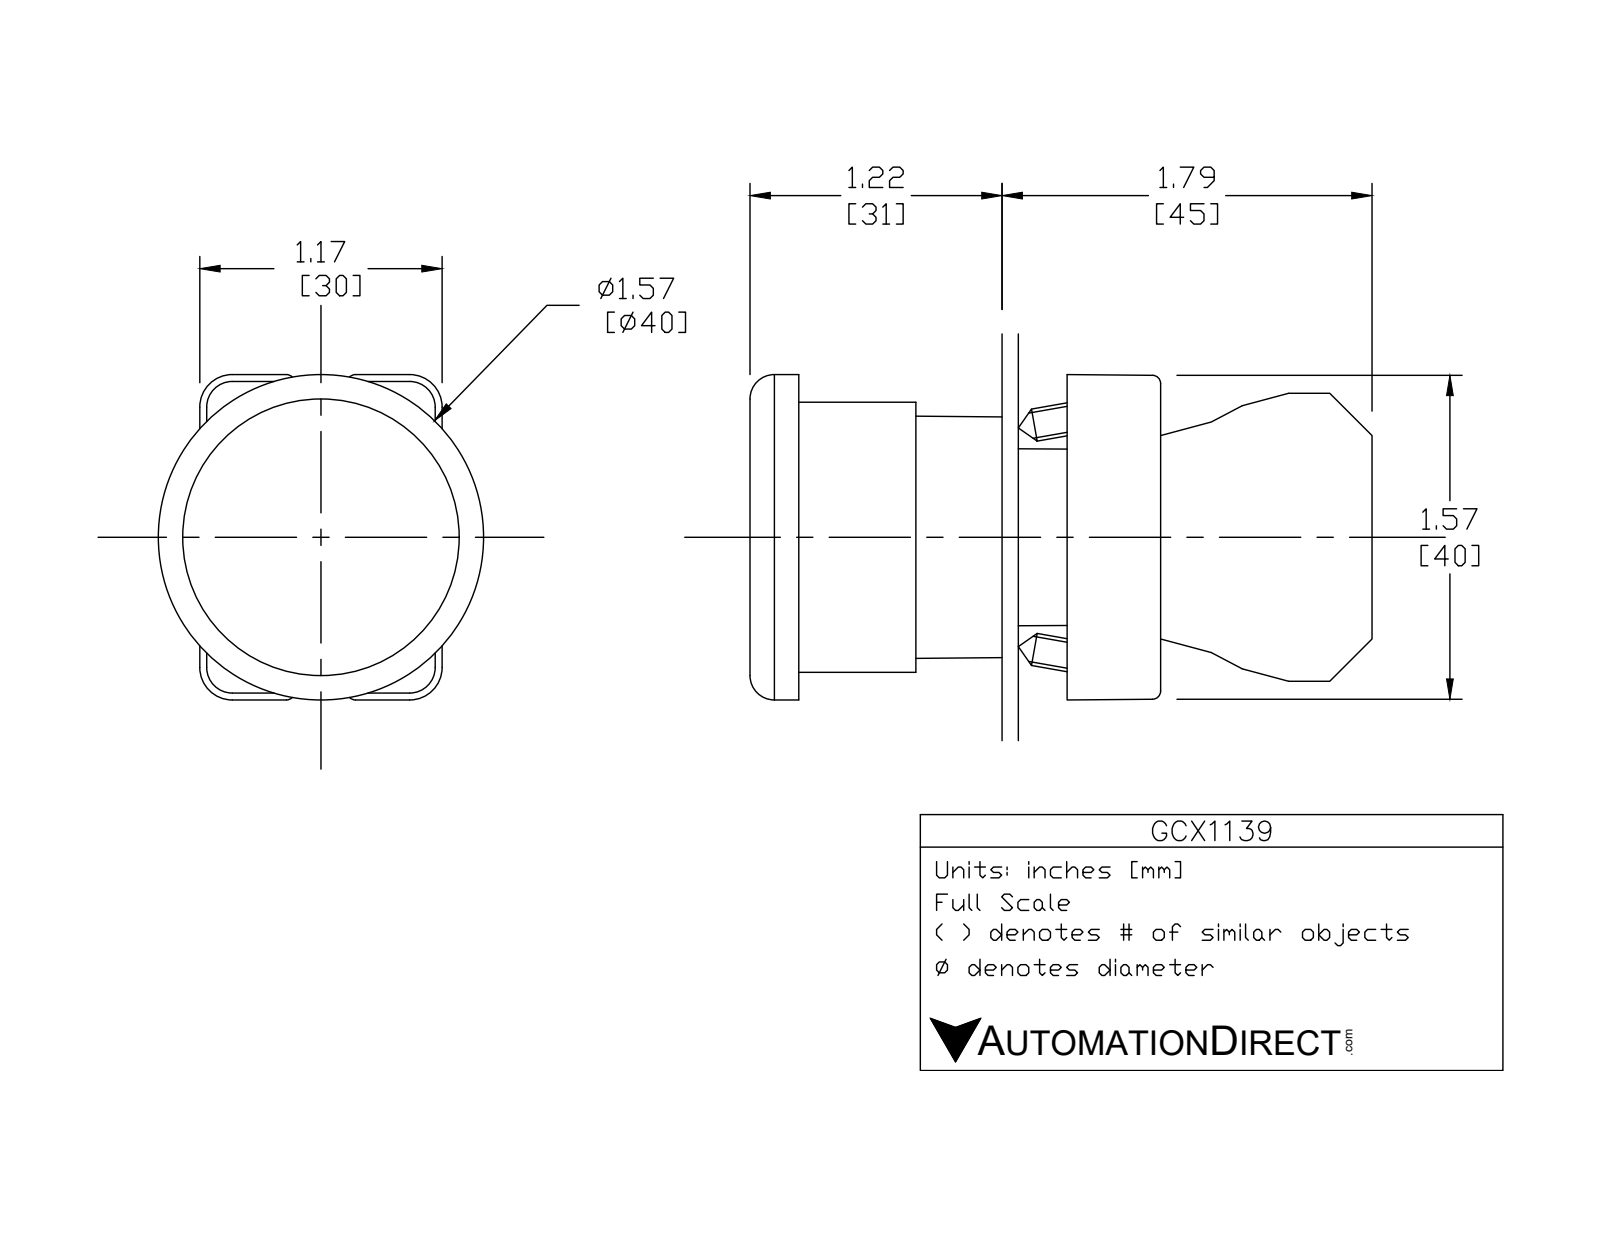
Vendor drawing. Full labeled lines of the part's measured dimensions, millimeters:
Part name (STEP PRODUCT): ecx1040; ECX1029-2; GCX1139 OPERATOR; GCX1139
STEP written by: SolidWorks 2016 (AUTOMOTIVE_DESIGN)
Units: millimetres
Bodies: 6 solids, 389 faces (224 planar, 136 cylindrical, 29 other)
Overall size (bounding box): 74.8 × 40.2 × 40
Volume: 30 660 mm³ · Surface area: 21 660 mm²
Round holes (diameter × count): ⌀2 ×2, ⌀3.1 ×2, ⌀3.3 ×2, ⌀2.2 ×1, ⌀5 ×1, ⌀22.3 ×1, ⌀22.6 ×1, ⌀26 ×1, ⌀30 ×1
Round bosses / shafts (diameter × count): ⌀4 ×2, ⌀40 ×1, ⌀33 ×1, ⌀29.8 ×1, ⌀24 ×1, ⌀21.7 ×1, ⌀19.8 ×1
Partial cylindrical surfaces — rounded edges, fillets, slot ends (radius × count): R1.5 ×24, R1 ×12, R3.1 ×12, R4 ×12, R1 ×4, R3.3 ×2, R0.5 ×1, R1.6 ×1
Main face-to-face distances: 48.8, 14.7, 0.8, 44.8, 4, 43.8, 0.8, 26, 19.3, 25.5
Hole centre spacings: 6, 13.8, 12, 12.4
